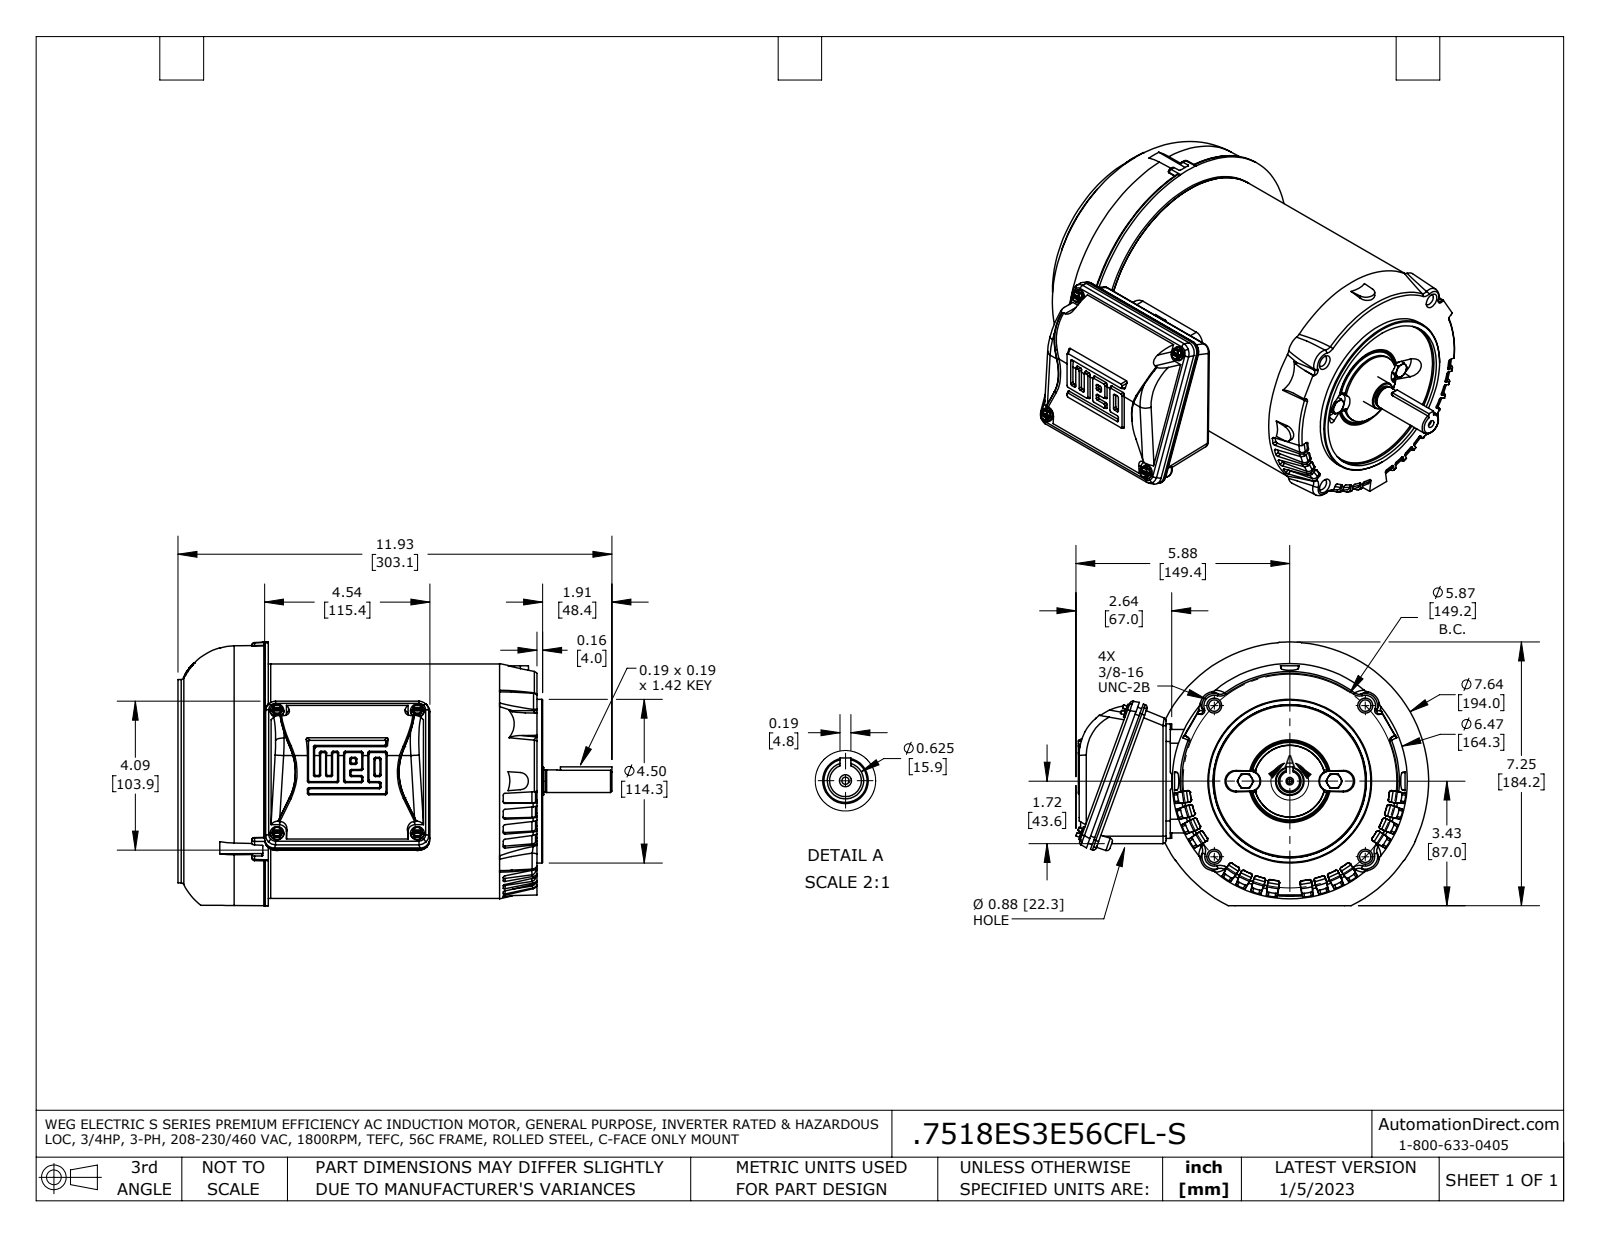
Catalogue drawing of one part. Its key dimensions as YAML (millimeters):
part_name: "56C_3PH_TEFC_GP_11929_FL fxt"
step_written_by: "SolidWorks 2021 (AUTOMOTIVE_DESIGN)"
units: millimeters
bodies: {solids: 13, faces: 1280, planar: 471, cylindrical: 275, other: 534}
overall_size: [303.1, 246.4, 191.8]
volume: 6045000
surface_area: 385200
round_holes:
  - {diameter: 8, count: 4}
  - {diameter: 3.1, count: 1}
round_bosses_or_shafts:
  - {diameter: 9.5, count: 4}
  - {diameter: 8.9, count: 2}
  - {diameter: 163.8, count: 1}
  - {diameter: 163.8, count: 1}
  - {diameter: 142, count: 1}
  - {diameter: 114.3, count: 1}
  - {diameter: 19.9, count: 1}
  - {diameter: 15.9, count: 1}
partial_cylinders:
  - {radius: 1.2, count: 40}
  - {radius: 0.2, count: 38}
  - {radius: 1.3, count: 32}
  - {radius: 1.5, count: 12}
  - {radius: 2.2, count: 12}
  - {radius: 0.5, count: 10}
  - {radius: 5.2, count: 8}
  - {radius: 7, count: 8}
face_to_face_distances: [160, 1.7, 161.7, 58, 59.7, 219.7, 245.7, 187.7, 186, 26]
hole_center_spacings: [74.6, 105.5, 149.2]
